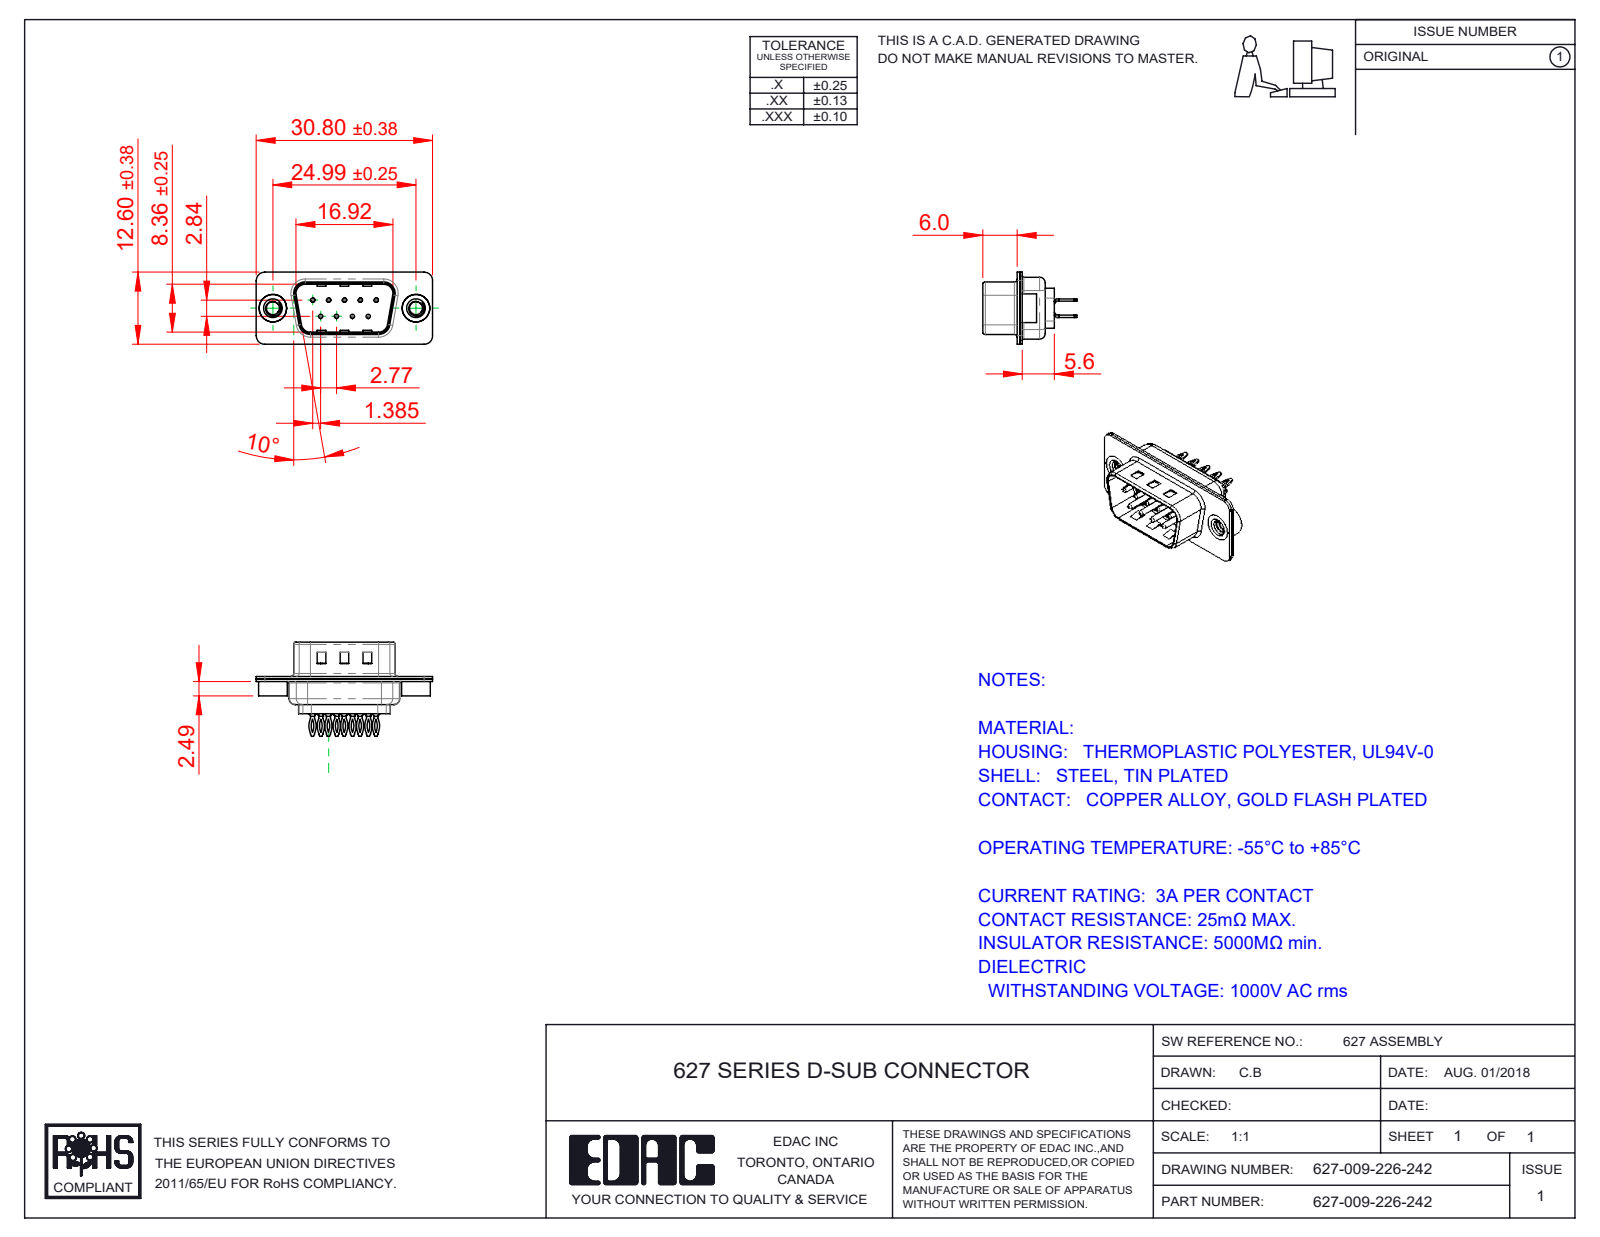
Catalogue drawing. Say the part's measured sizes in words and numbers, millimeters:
The part is named "627-009-226-242; 627 Shell Front_09 Contacts; 627 Contact Row 1_26L; 627 Contact Row 2_26L (+3 more)". Its 3-D file was written by "SolidWorks 2020 (CONFIG_CONTROL_DESIGN)". It is 14 solids with 984 faces: 287 planar, 406 cylindrical and 291 other. Overall it measures 30.8 by 16.45 by 12.6 millimeters. Its volume is 1 307 cubic millimeters and its surface area 3 895 square millimeters. Round holes: 9 of diameter 0.35, 9 of diameter 1.1, 9 of diameter 1.6, 2 of diameter 2.26, 2 of diameter 4, 2 of diameter 4.8. Round bosses or shafts: 9 of diameter 2, 9 of diameter 1.5, 9 of diameter 0.75, 2 of diameter 5, 2 of diameter 4.9. Partial cylindrical surfaces (rounded edges, fillets, slot ends): 18 of radius 1.5, 18 of radius 2.92, 18 of radius 3.33, 12 of radius 2, 8 of radius 0.5, 8 of radius 1.6, 4 of radius 0.25, 4 of radius 0.6. The main face-to-face distances are 0.4, 0.45, 0.9, 0.82, 9.58, 1.4, 8.76, 0.5, 1.5, 6.05. The hole center spacings are 3.16, 2.77, 5.54, 5.03, 5.04, 8.31, 7.48, 7.49.
